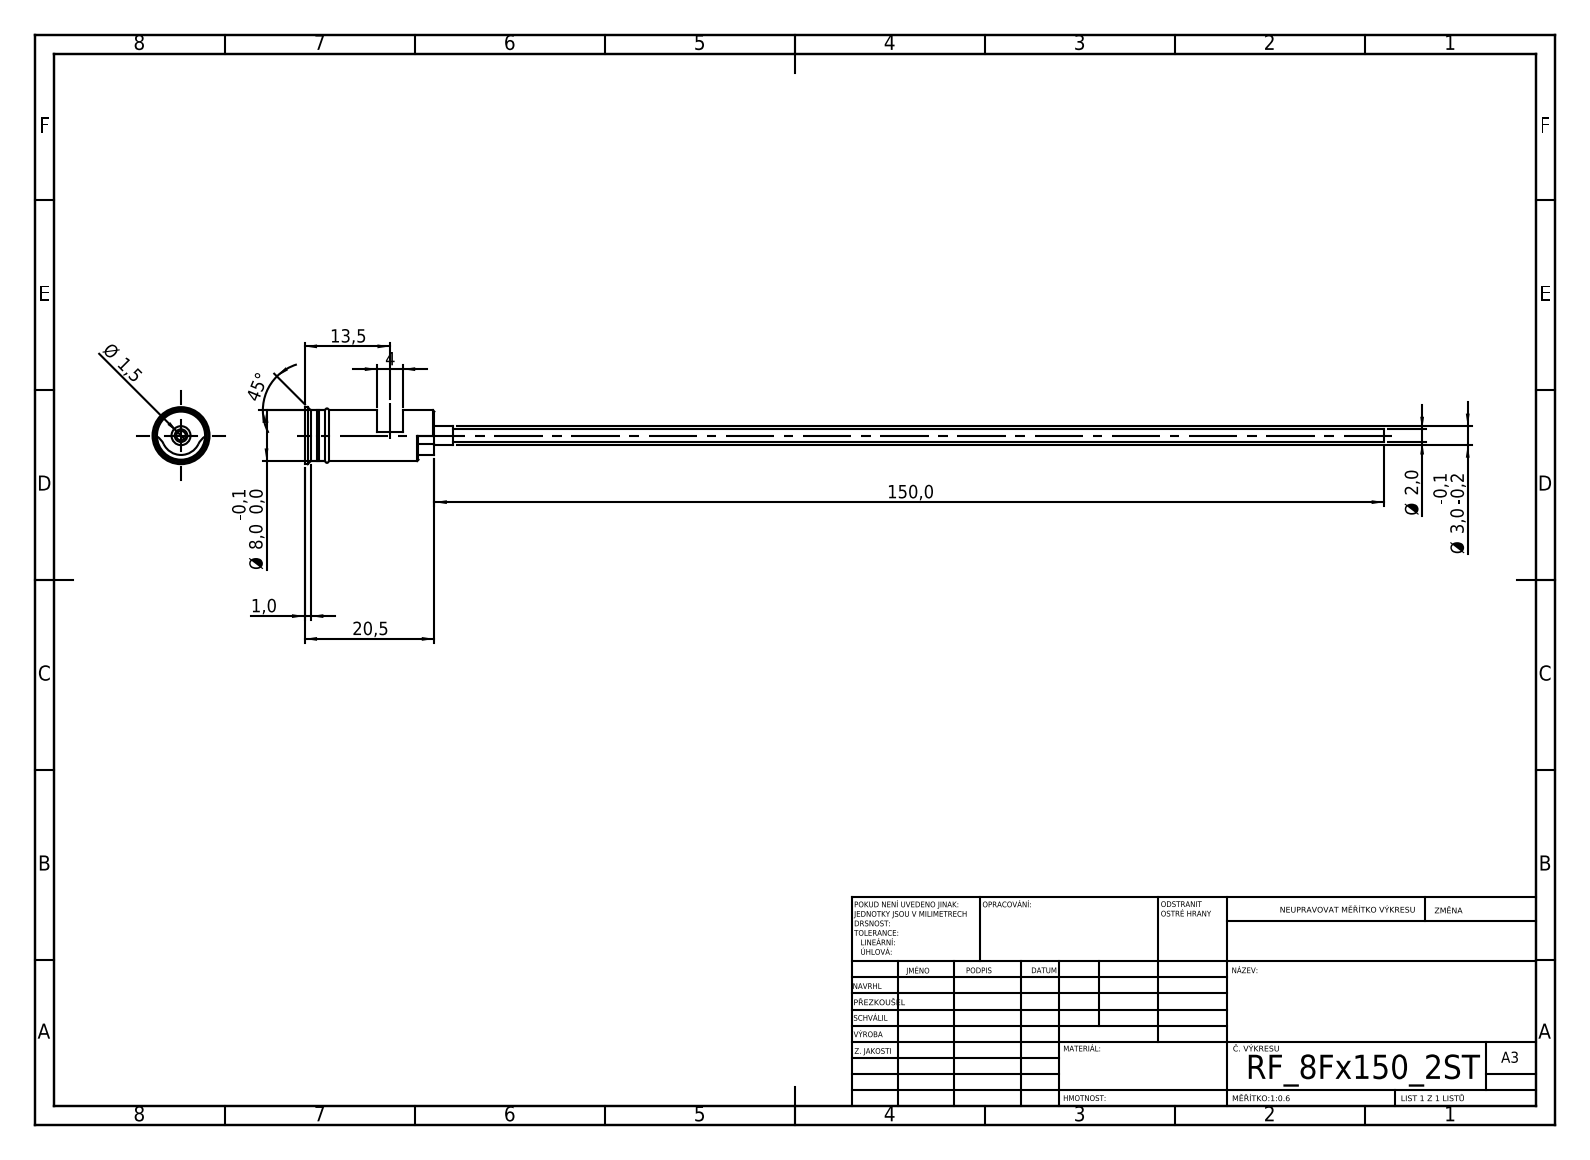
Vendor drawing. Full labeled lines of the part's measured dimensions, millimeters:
STEP written by: SolidWorks 2019 (CONFIG_CONTROL_DESIGN)
Units: millimetres
Bodies: 1 solid, 55 faces (24 planar, 19 cylindrical, 12 other)
Overall size (bounding box): 170.5 × 9 × 9
Volume: 1 111 mm³ · Surface area: 2 390 mm²
Round holes (diameter × count): ⌀1.5 ×1
Round bosses / shafts (diameter × count): ⌀9 ×1, ⌀8 ×1, ⌀7.8 ×1, ⌀3 ×1, ⌀2 ×1
Partial cylindrical surfaces — rounded edges, fillets, slot ends (radius × count): R3 ×2, R3.05 ×1
Main face-to-face distances: 4, 20.5, 9, 11.5, 5, 15.5, 2.5, 18.5, 13.5, 9.5
